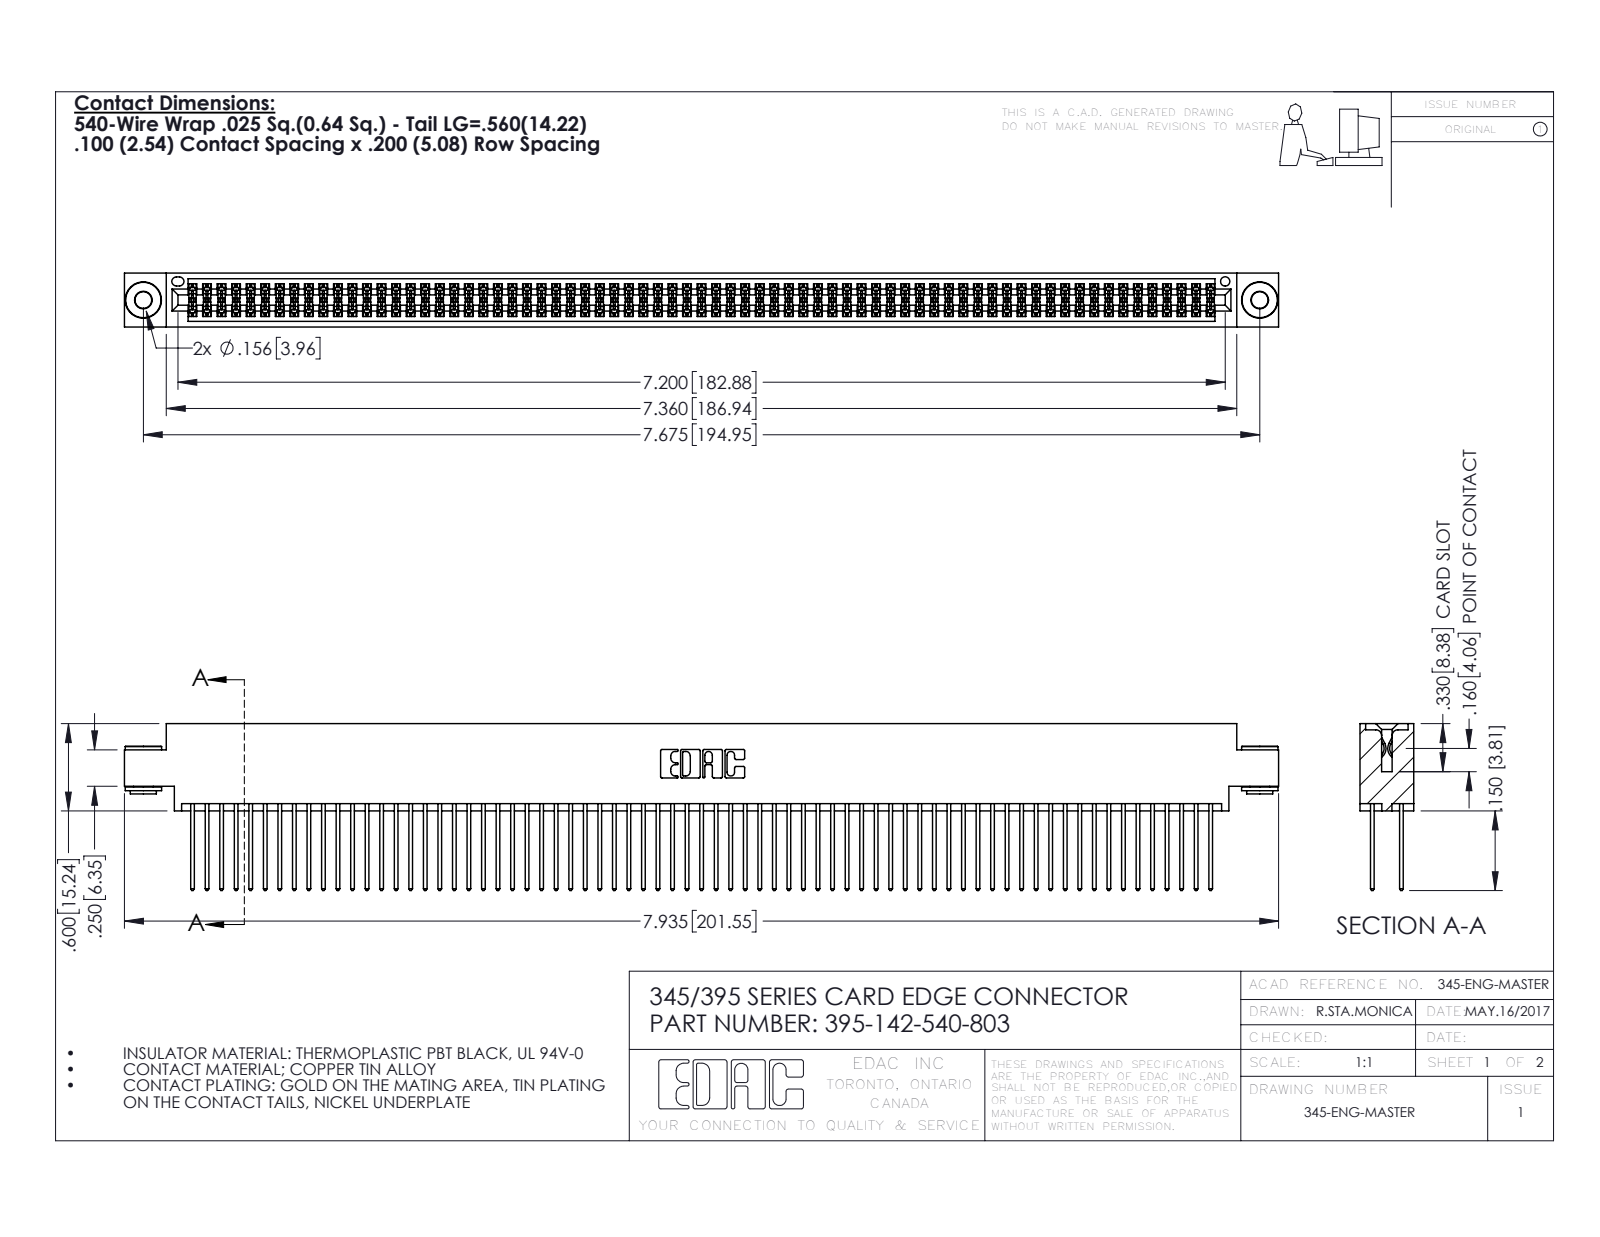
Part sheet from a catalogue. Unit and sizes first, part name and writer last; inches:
Units: inches
Overall size (bounding box): 7.935 × 1.147 × 0.37
Round holes (diameter × count): ⌀0.116 ×2, ⌀0.156 ×2, ⌀0.064 ×1
Round bosses / shafts (diameter × count): ⌀0.25 ×2, ⌀0.18 ×2, ⌀0.136 ×2
Partial cylindrical surfaces — rounded edges, fillets, slot ends (radius × count): R0.006 ×213, R0.01 ×142, R0.01 ×22, R0.007 ×6, R0.031 ×6, R0.026 ×3, R0.014 ×2, R0.019 ×2
Main face-to-face distances: 0.072, 0.298, 0.2, 0.098, 0.272, 0.025, 0.37, 0.225, 0.175, 0.149
Hole centre spacings: 0.27, 7.439, 7.675
Volume: 1.238 in³ · Surface area: 51.77 in²
Bodies: 145 solids, 7268 faces (4780 planar, 2480 cylindrical, 8 other)
Part name (STEP PRODUCT): 345-292-001_345-293-140; 345-250-002_345-250-002-102; 345 Part_0.170 Offset - 0.156 Dia-TH; 395-142-540-803
STEP written by: SolidWorks 2016 (CONFIG_CONTROL_DESIGN)
